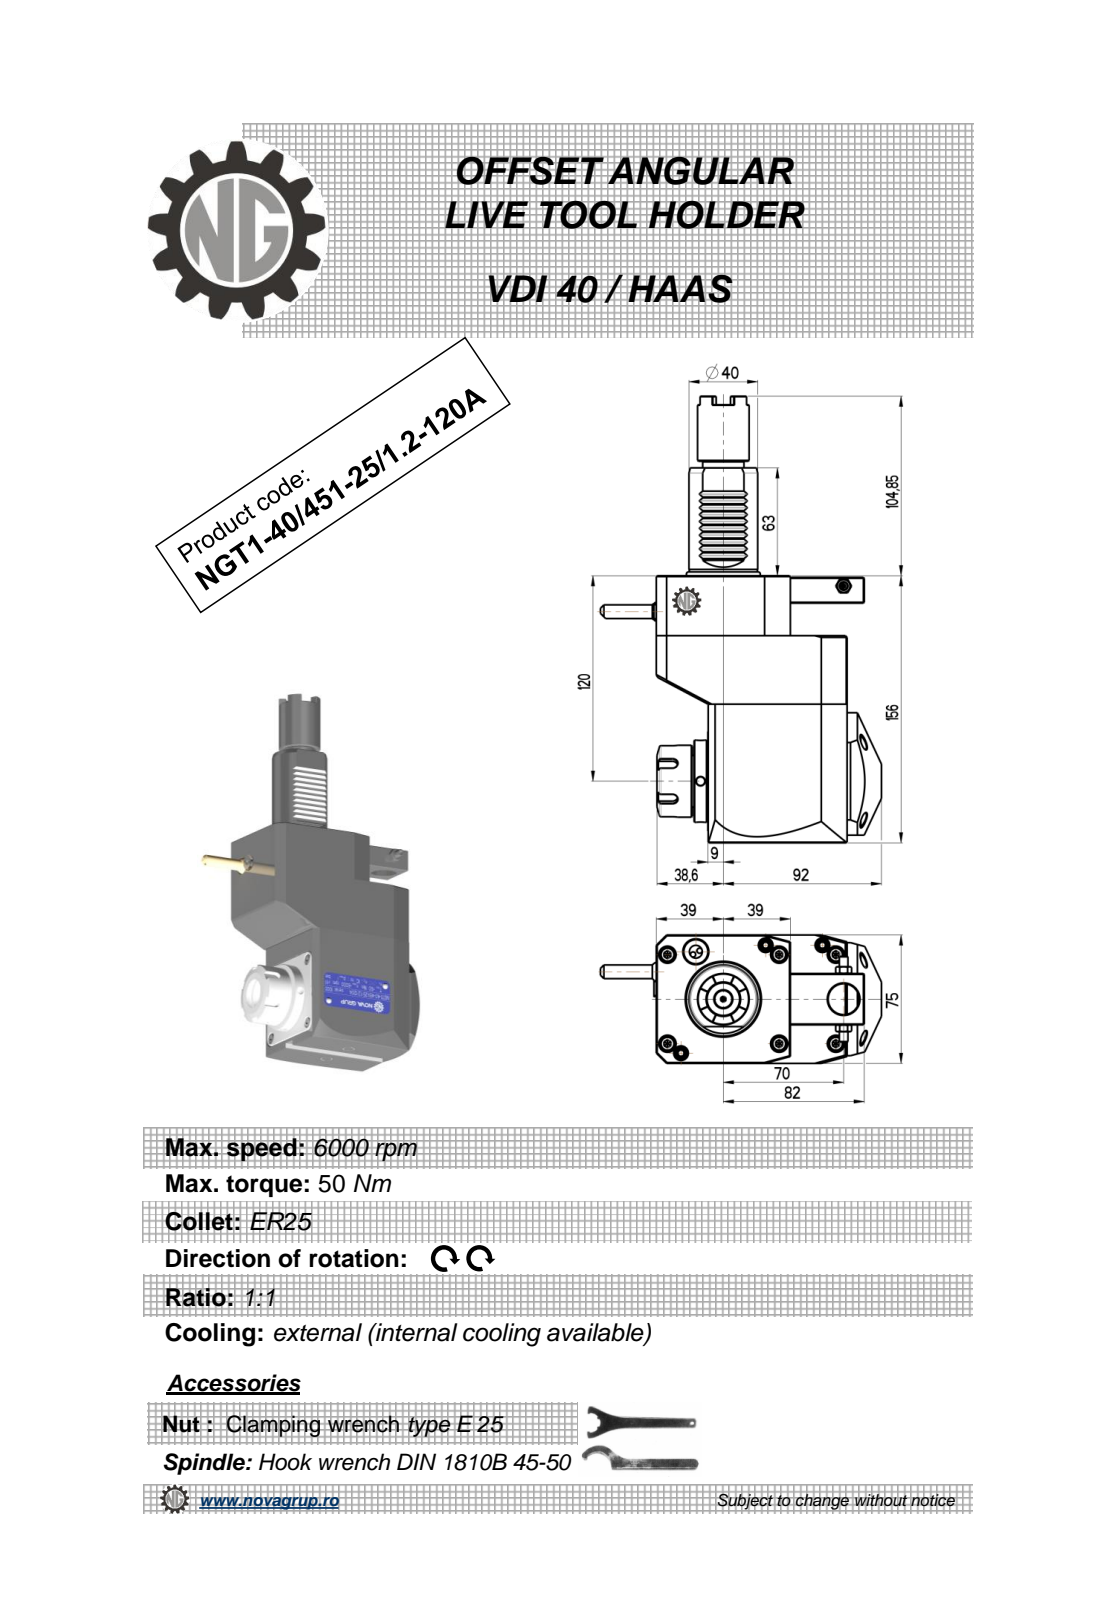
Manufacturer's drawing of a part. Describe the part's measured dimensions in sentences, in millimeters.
The part is named "NGT1_40_451_25_1_2_120A". Its 3-D file was written by "PRO/ENGINEER BY PARAMETRIC TECHNOLOGY CORPORATION, 2010280 (CONFIG_CONTROL_DESIGN)". It is 1 solid with 487 faces: 231 planar, 97 cylindrical and 159 other. Overall it measures 260.85 by 163.5 by 76.6 millimeters. Its volume is 1 205 000 cubic millimeters and its surface area 92 967 square millimeters. Round holes: 3 of diameter 5, 1 of diameter 3, 1 of diameter 4.2, 1 of diameter 9.5, 1 of diameter 18, 1 of diameter 20.3, 1 of diameter 26.8. Round bosses or shafts: 1 of diameter 48, 1 of diameter 42, 1 of diameter 40, 1 of diameter 37.5, 1 of diameter 33, 1 of diameter 30, 1 of diameter 26.58, 1 of diameter 24. Partial cylindrical surfaces (rounded edges, fillets, slot ends): 12 of radius 0.26, 10 of radius 0.3, 6 of radius 0.2, 5 of radius 3, 1 of radius 0.5, 1 of radius 9.75, 1 of radius 40. The main face-to-face distances are 75, 156, 111, 30, 121, 35, 81, 33, 48, 78. The hole center spacings are 13.25, 20.93, 70, 83.25, 100.28, 112.5, 141.16.
